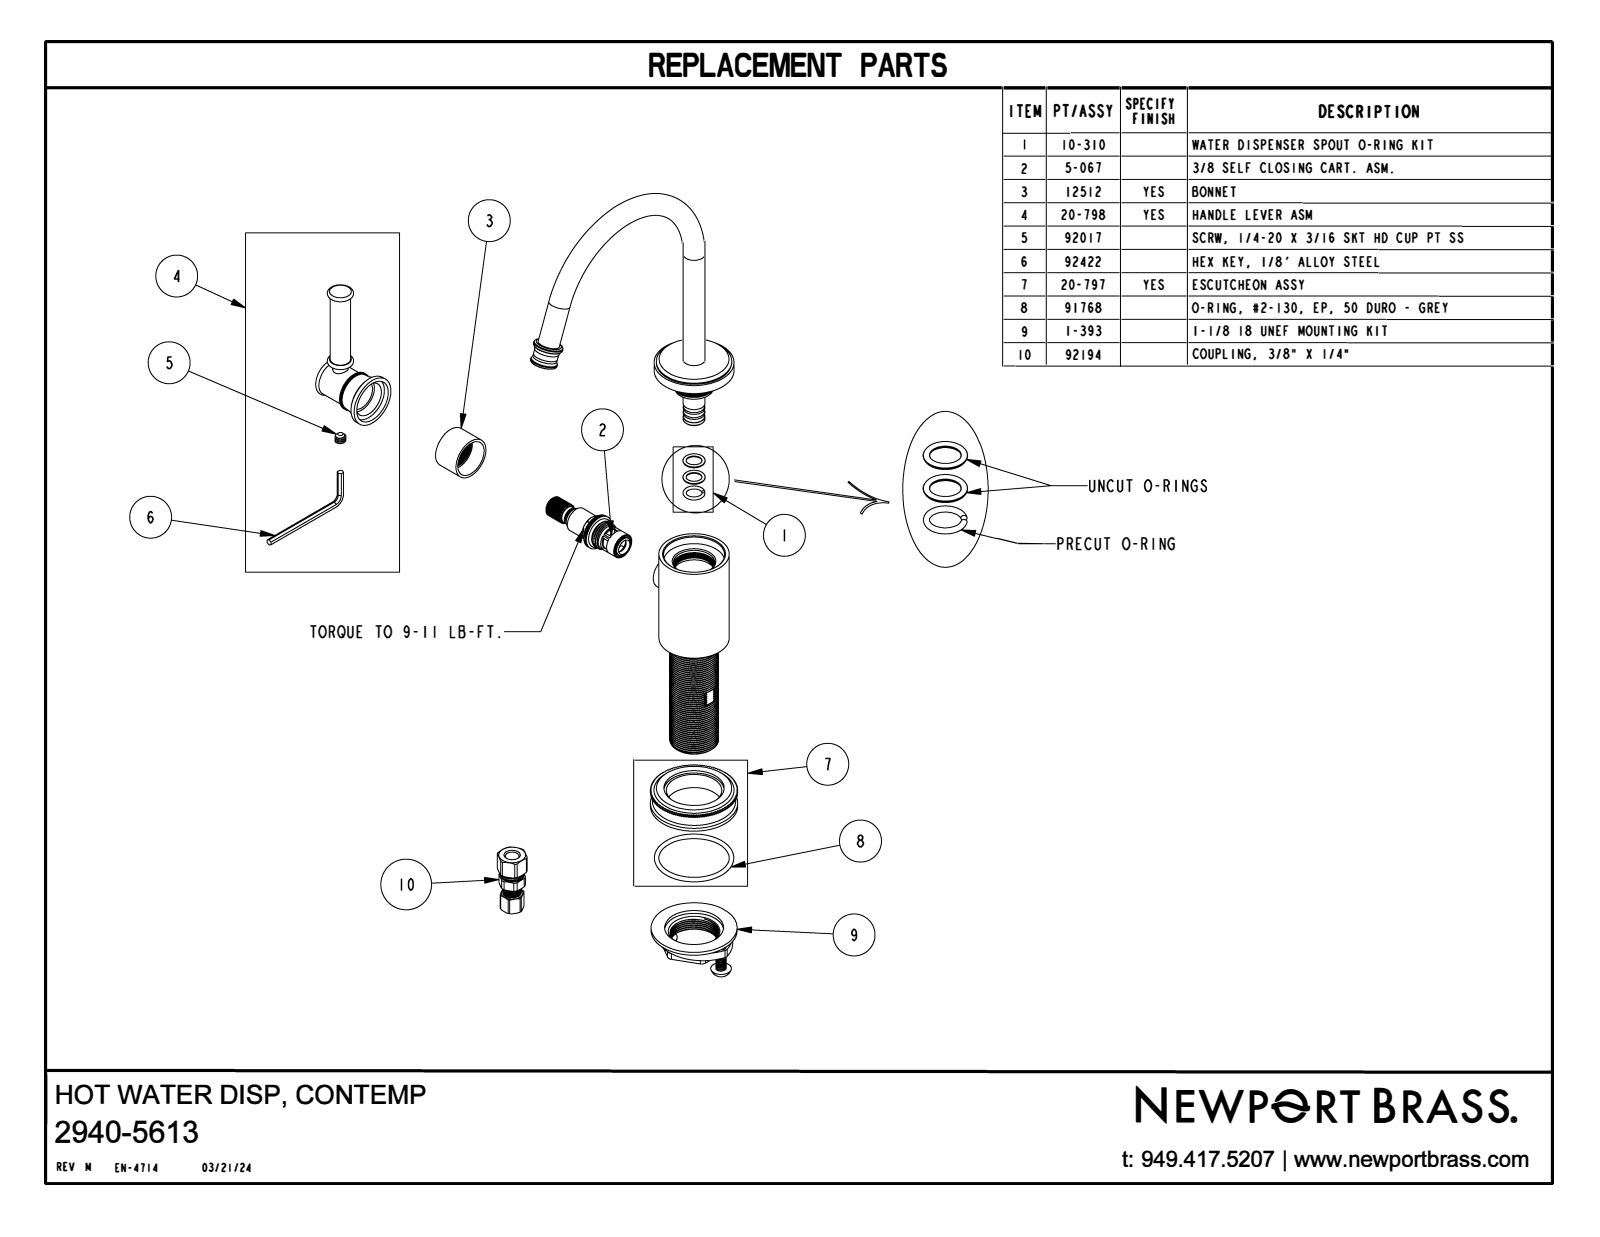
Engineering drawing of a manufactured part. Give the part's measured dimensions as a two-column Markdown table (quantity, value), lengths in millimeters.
| quantity | value |
| --- | --- |
| part name | 2940-5613 |
| STEP written by | CREO PARAMETRIC BY PTC INC, 2018400 (CONFIG_CONTROL_DESIGN) |
| units | millimeters |
| bodies | 1 solid, 681 faces (409 planar, 226 cylindrical, 46 other) |
| overall size | 243.1 × 153.8 × 89.4 |
| volume | 179 800 mm³ |
| surface area | 34 380 mm² |
| round holes (diameter × count) | 25.4 × 1 |
| round bosses / shafts (diameter × count) | 12.7 × 2, 50.8 × 1, 48.4 × 1, 46.5 × 1, 43.9 × 1, 40.9 × 1, 30.2 × 1, 27.9 × 1 |
| partial cylindrical surfaces (radius × count) | 4.5 × 1, 11.9 × 1 |
| main face-to-face distances | 81.9, 11.3, 70.6, 12.7, 9.8, 72.1, 36.1, 1.4, 69.2, 73.8 |
